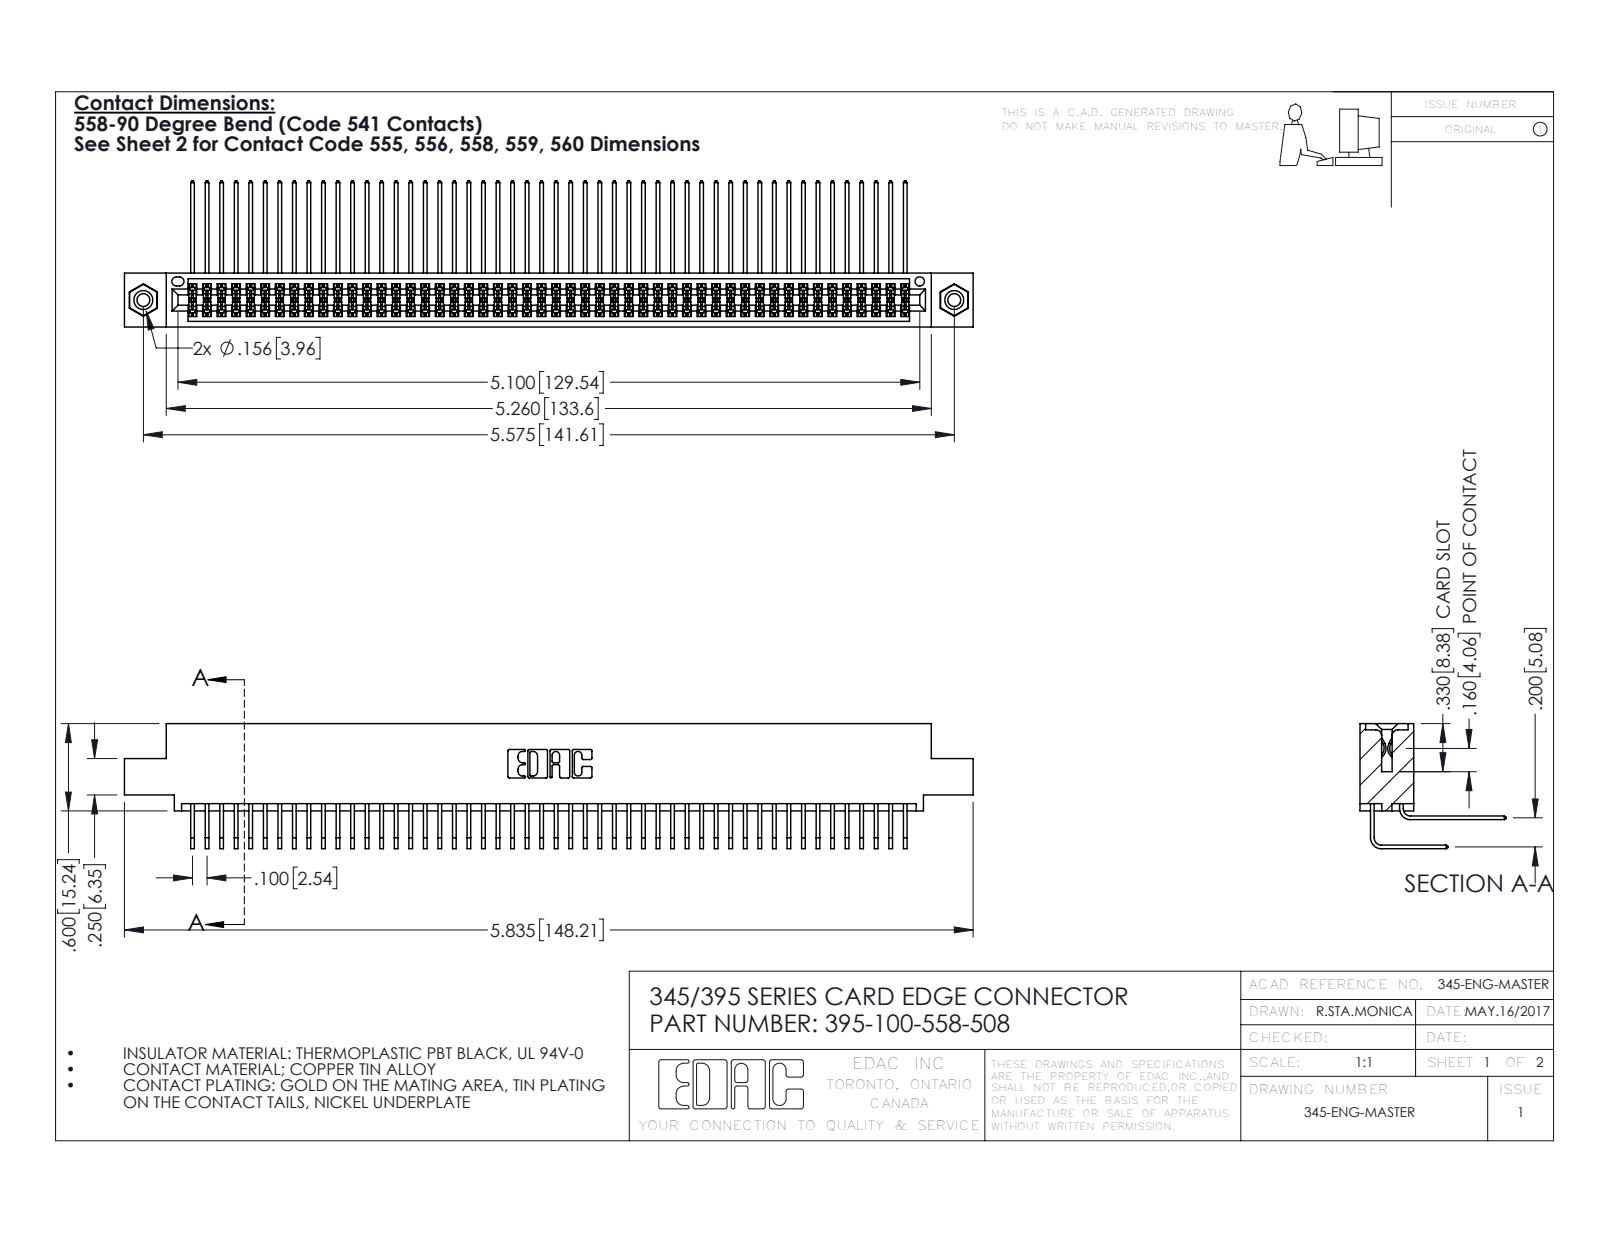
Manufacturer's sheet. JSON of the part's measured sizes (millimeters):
{"part_name": "395-100-558-508; 345-250-001_345-250-003-102; 345 Part_0.110 Offset - 0.156 Dia-TI; 345-292-001_558 559 Tail - 1 (+1 more)", "step_written_by": "SolidWorks 2016 (CONFIG_CONTROL_DESIGN)", "units": "millimeters", "bodies": {"solids": 103, "faces": 5390, "planar": 3616, "cylindrical": 1758, "other": 16}, "overall_size": [148.2, 25.5, 21.8], "volume_mm3": 15000, "surface_area_mm2": 25100, "round_holes": [[2.3, 2], [3.2, 2], [4, 2], [1.6, 1]], "round_bosses_or_shafts": [[3.9, 2]], "partial_cylinders_radius": [[0.2, 151], [0.3, 22], [0.2, 6], [0.8, 6], [0.7, 3], [0.4, 2], [0.5, 2], [0.6, 2]], "face_to_face_distances": [1.8, 7.6, 5.1, 9.4, 2.5, 6.9, 0.6, 5.7, 0.6, 4.4], "hole_center_spacings": [6.9, 135.6, 141.6]}
